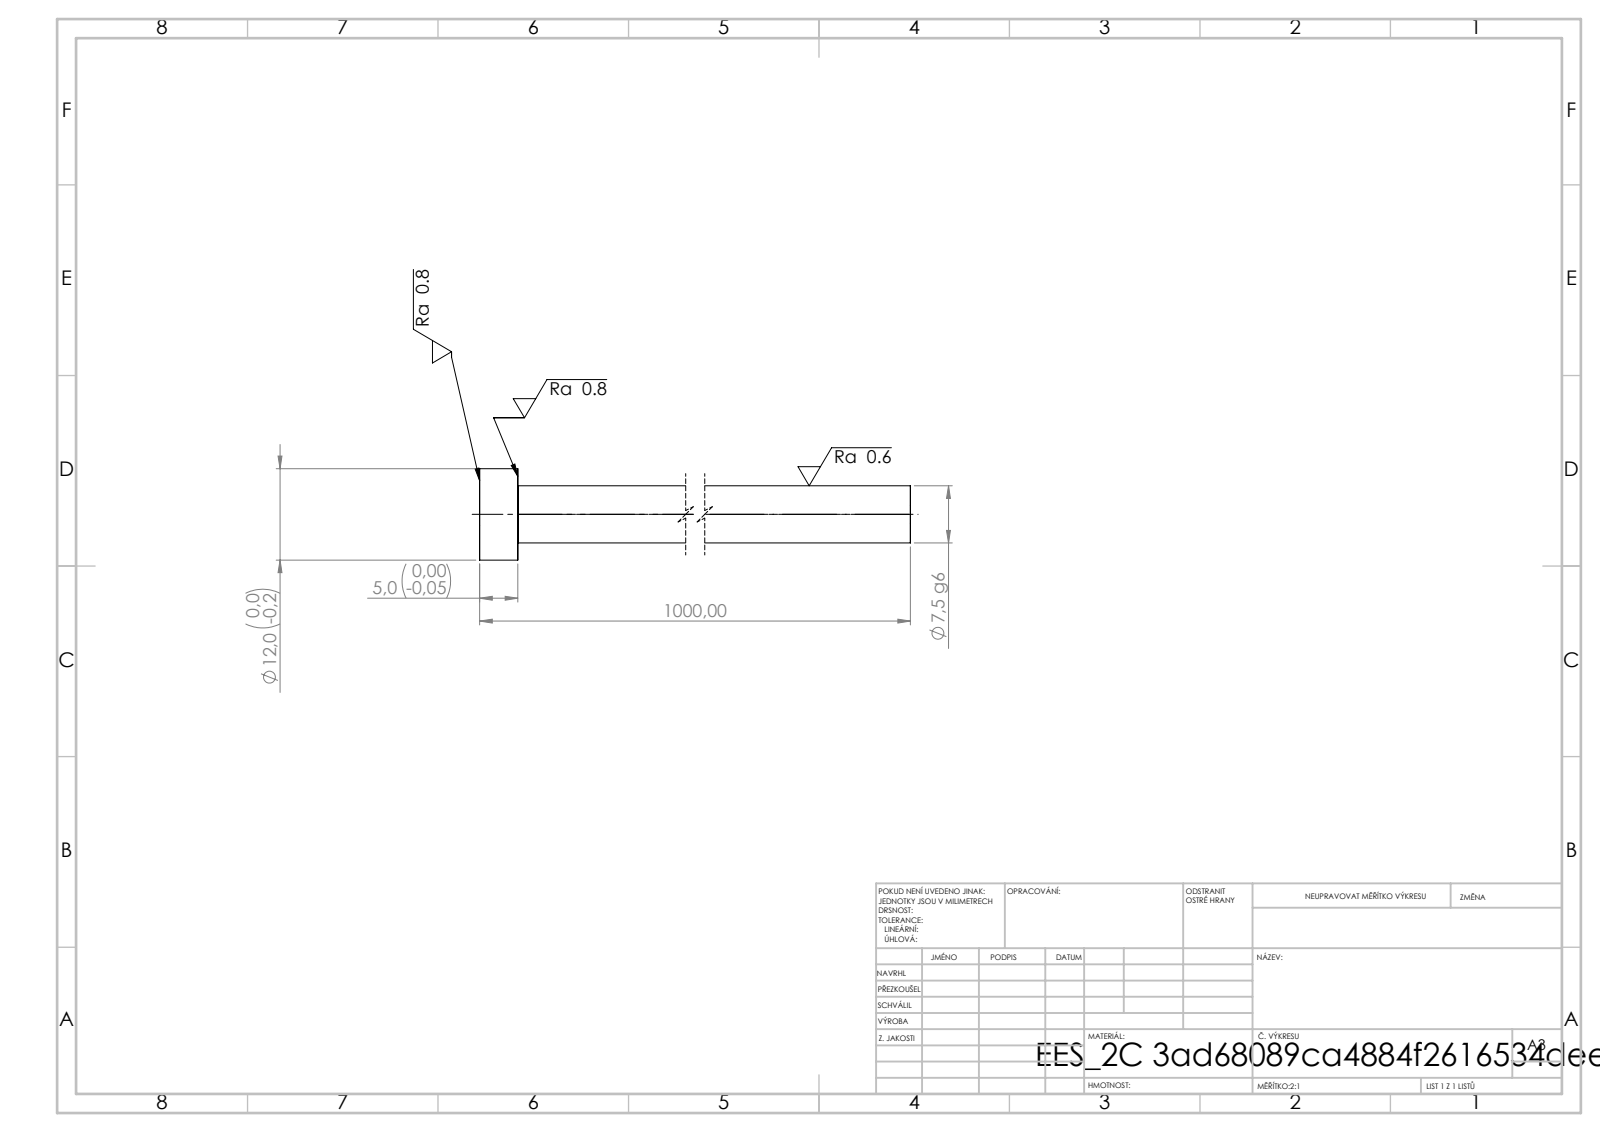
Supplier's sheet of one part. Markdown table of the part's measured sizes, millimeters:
| quantity | value |
| --- | --- |
| STEP written by | SolidWorks 2019 (CONFIG_CONTROL_DESIGN) |
| units | millimeters |
| bodies | 1 solid, 7 faces (3 planar, 4 cylindrical, 0 other) |
| overall size | 1000 × 12 × 12 |
| volume | 44 523 mm³ |
| surface area | 23 859 mm² |
| round bosses / shafts (diameter × count) | 12 × 1, 7.5 × 1 |
| main face-to-face distances | 5, 1000, 995 |
